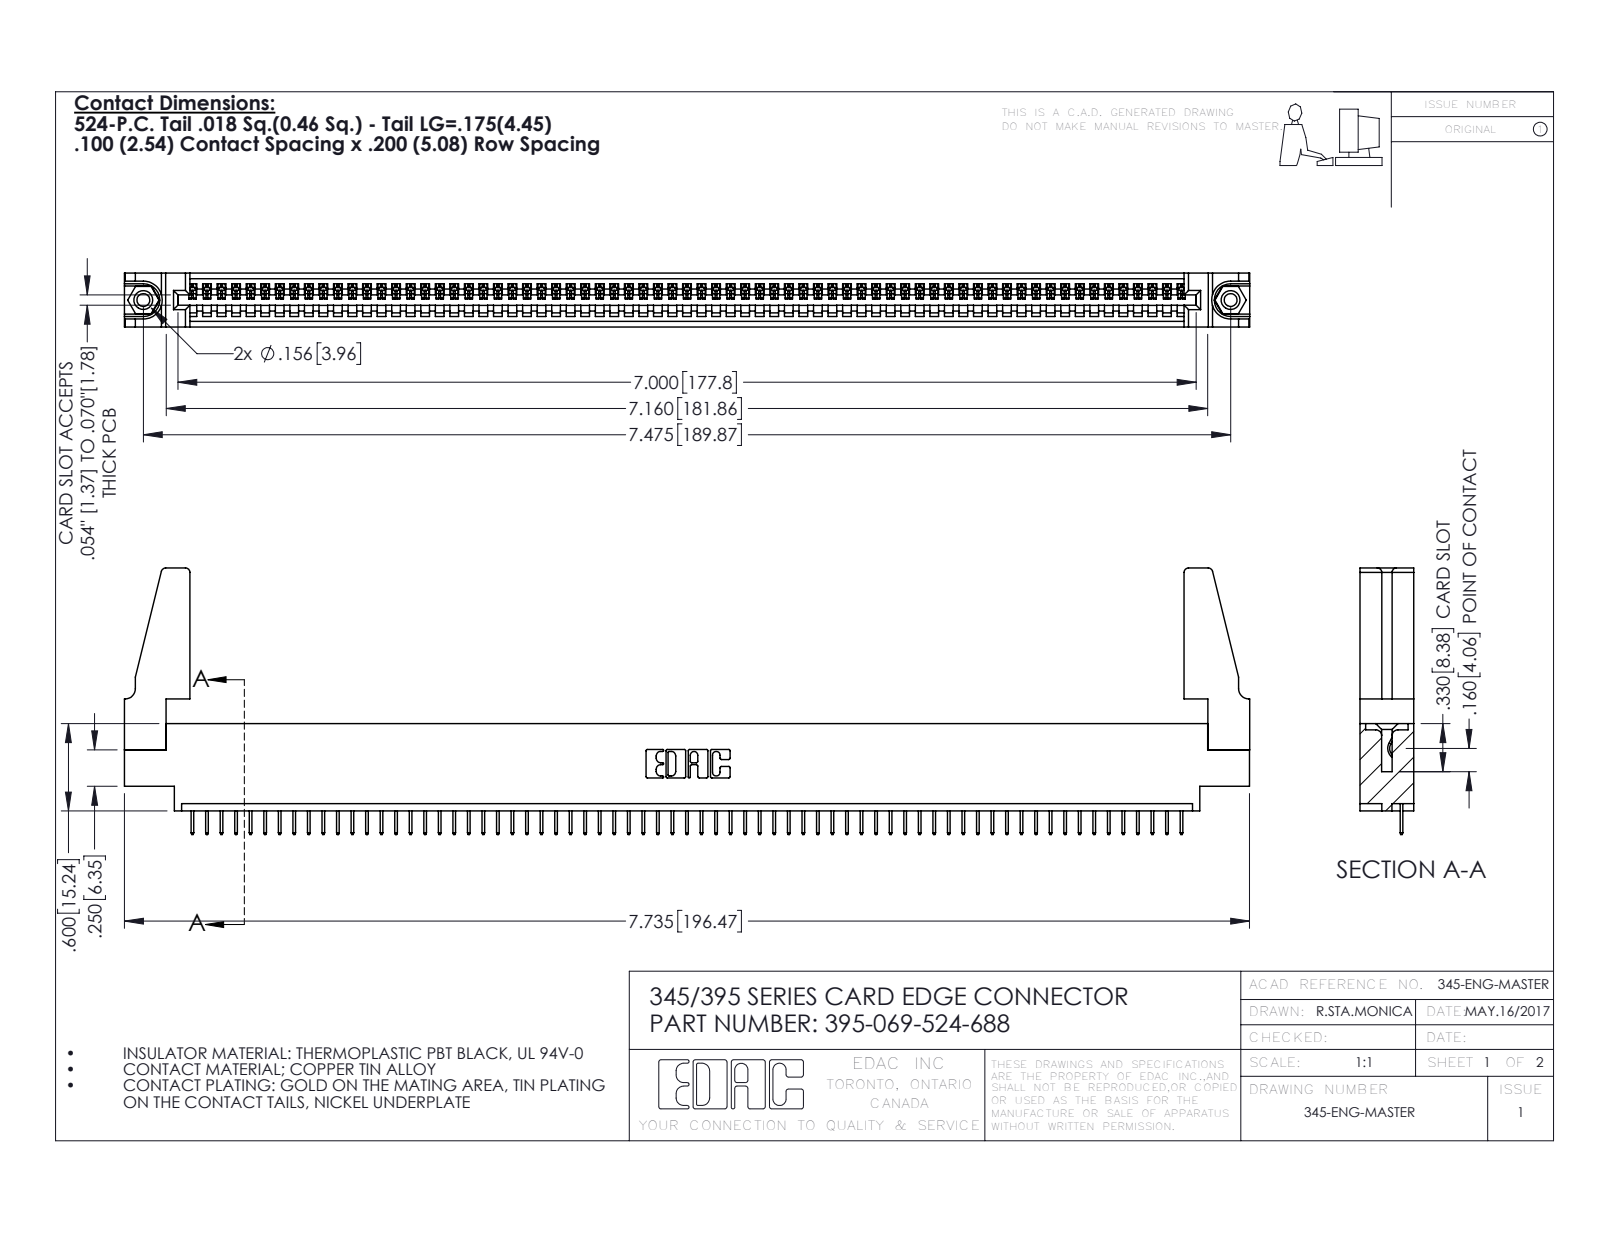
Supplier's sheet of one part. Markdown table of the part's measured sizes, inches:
| quantity | value |
| --- | --- |
| part name | 345-220-078_345-220-088; 395-069-524-688; 345-250-001_345-250-001-102; 345-292-001_345-293-124 (+1 more) |
| STEP written by | SolidWorks 2016 (CONFIG_CONTROL_DESIGN) |
| units | inches |
| bodies | 74 solids, 4532 faces (3330 planar, 1186 cylindrical, 16 other) |
| overall size | 7.736 × 1.832 × 0.37 |
| volume | 1.327 in³ |
| surface area | 42.37 in² |
| round holes (diameter × count) | 0.089 × 2, 0.125 × 2, 0.156 × 2, 0.064 × 1 |
| round bosses / shafts (diameter × count) | 0.155 × 2 |
| partial cylindrical surfaces (radius × count) | 0.006 × 138, 0.01 × 22, 0.03 × 8, 0.007 × 6, 0.031 × 6, 0.026 × 3, 0.031 × 2, 0.04 × 2 |
| main face-to-face distances | 0.072, 0.298, 0.37, 0.098, 0.272, 0.025, 0.2, 0.225, 0.072, 0.175 |
| hole center spacings | 0.27, 7.239, 7.475 |
